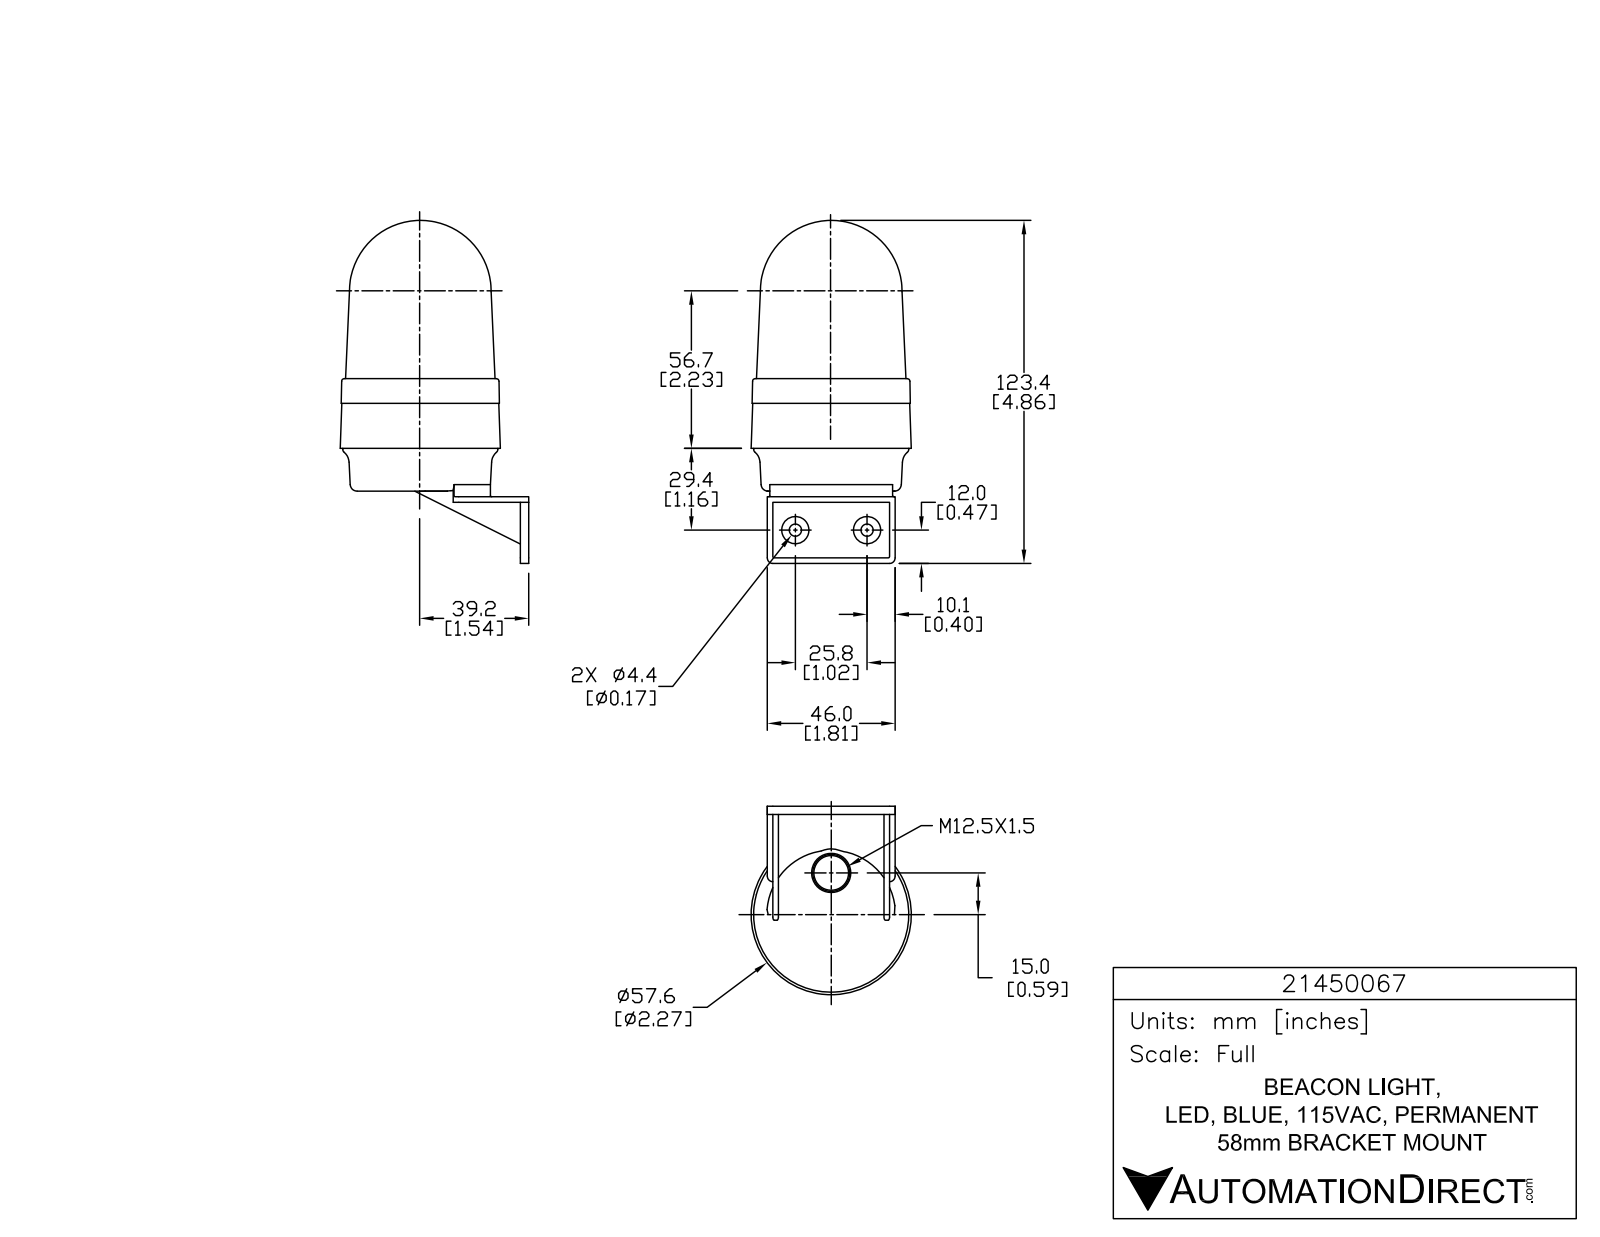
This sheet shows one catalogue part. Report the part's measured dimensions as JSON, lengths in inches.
{"part_name": "21450067", "step_written_by": "SolidWorks 2015 (AUTOMOTIVE_DESIGN)", "units": "inches", "bodies": {"solids": 1, "faces": 828, "planar": 551, "cylindrical": 179, "other": 98}, "overall_size": [4.858, 2.852, 2.407], "volume_in3": 12.43, "surface_area_in2": 37.49, "round_holes": [[0.039, 3], [0.173, 2]], "round_bosses_or_shafts": [[0.226, 3], [0.056, 3], [0.386, 2], [2.197, 1]], "partial_cylinders_radius": [[0.008, 6], [0.008, 6], [0.008, 6], [0.02, 6], [0.131, 6], [0.079, 4], [0.004, 3], [0.005, 3]], "face_to_face_distances": [0.079, 0.157, 1.575, 1.654, 0.039, 0.118, 1.496, 0.866, 0.945, 0.764], "hole_center_spacings": [1.016]}
